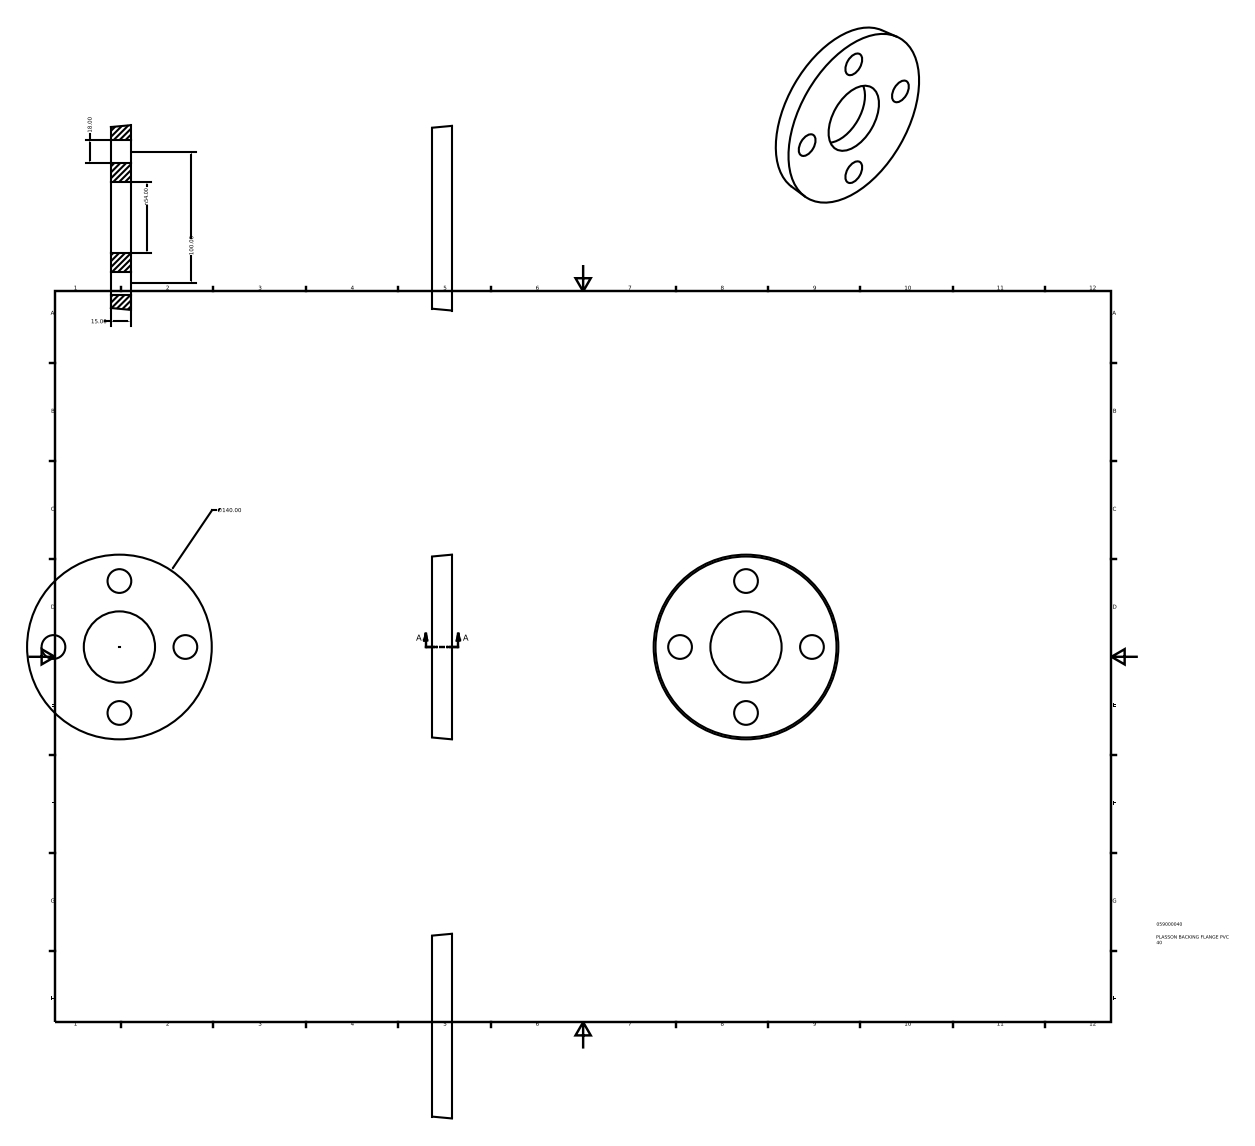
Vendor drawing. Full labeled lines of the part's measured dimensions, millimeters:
Part name (STEP PRODUCT): 059000040
STEP written by: Autodesk Inventor 2015 (AUTOMOTIVE_DESIGN)
Units: millimetres
Bodies: 1 solid, 8 faces (2 planar, 5 cylindrical, 1 other)
Overall size (bounding box): 140 × 140 × 15
Volume: 176 698 mm³ · Surface area: 36 059 mm²
Round holes (diameter × count): ⌀18 ×4, ⌀54 ×1
Main face-to-face distances: 15
Hole centre spacings: 50, 70.71, 100
